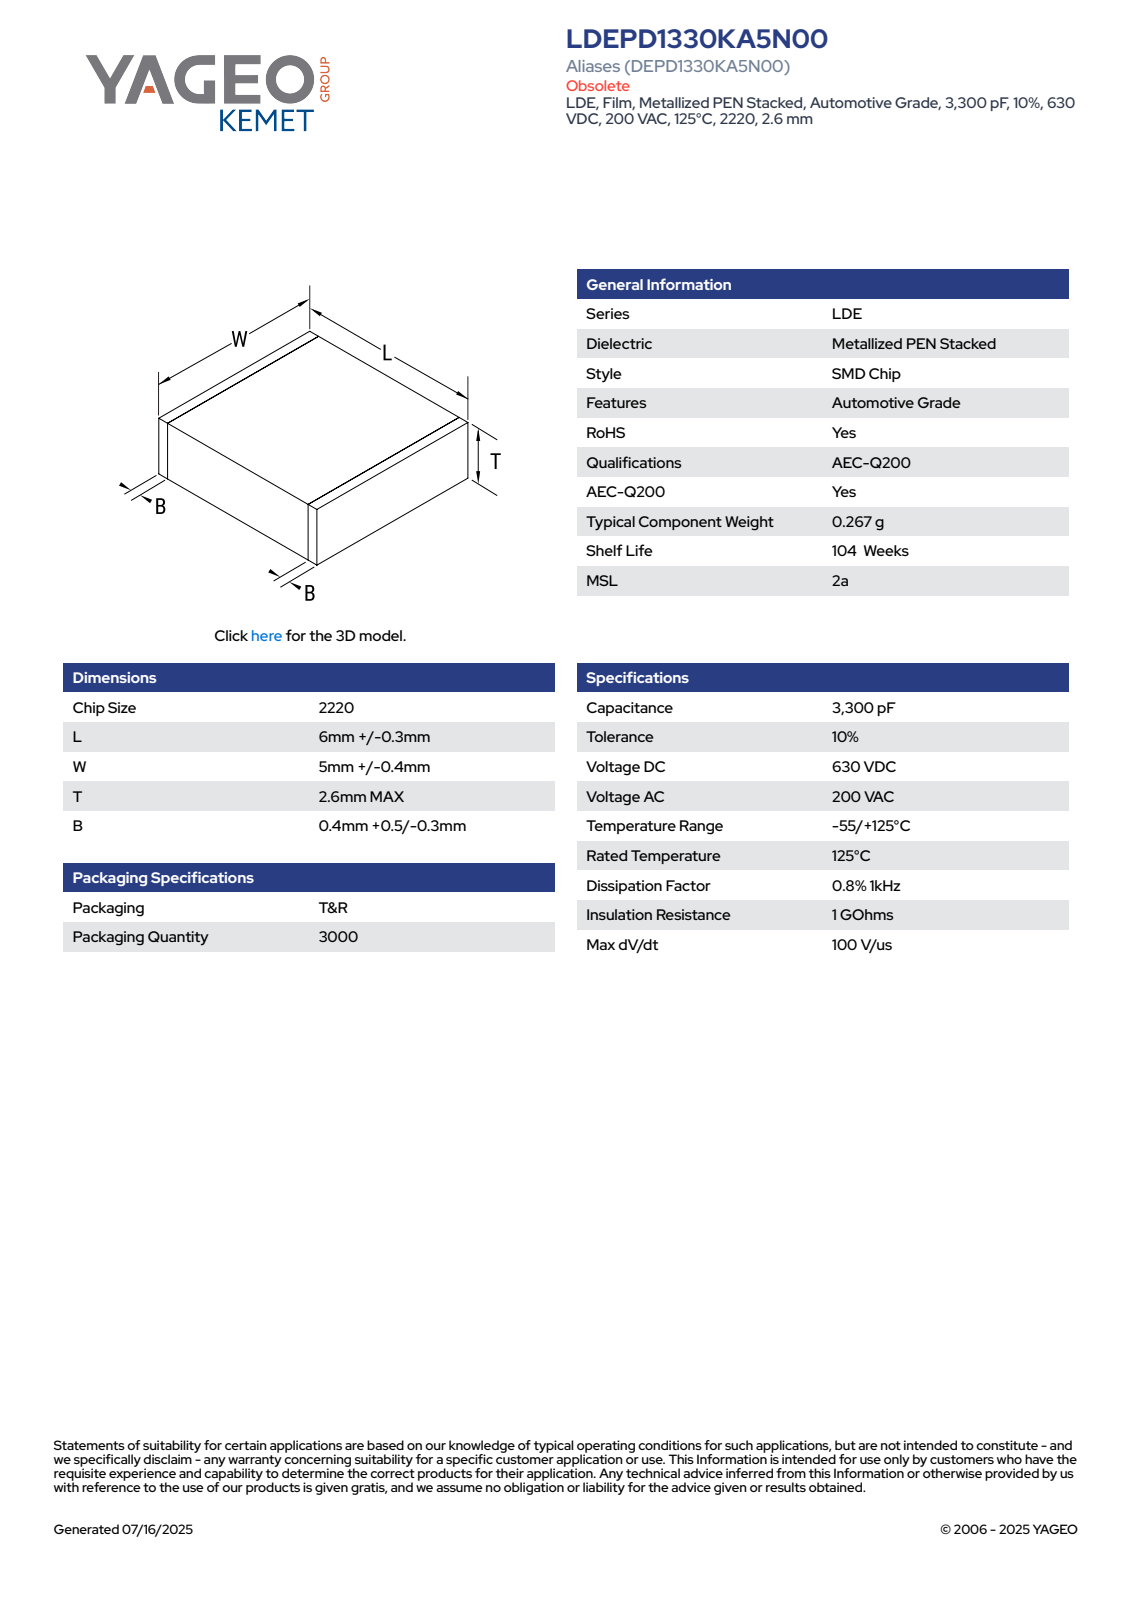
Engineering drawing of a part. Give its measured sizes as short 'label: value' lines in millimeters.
name: CFS_LDELDB_2220_L6.3W5.4T2.6B0.9
written by: SolidWorks 2020 (AUTOMOTIVE_DESIGN)
unit: mm
bodies: 4 solids, 73 faces (73 planar, 0 cylindrical, 0 other)
size: 6.3 × 5.4 × 2.6
volume: 88 mm³; area: 131 mm²
face distances: 2.58, 6.3, 5.38, 2.59, 2.6, 5.39, 5.4, 0.5, 5.8, 5.3
